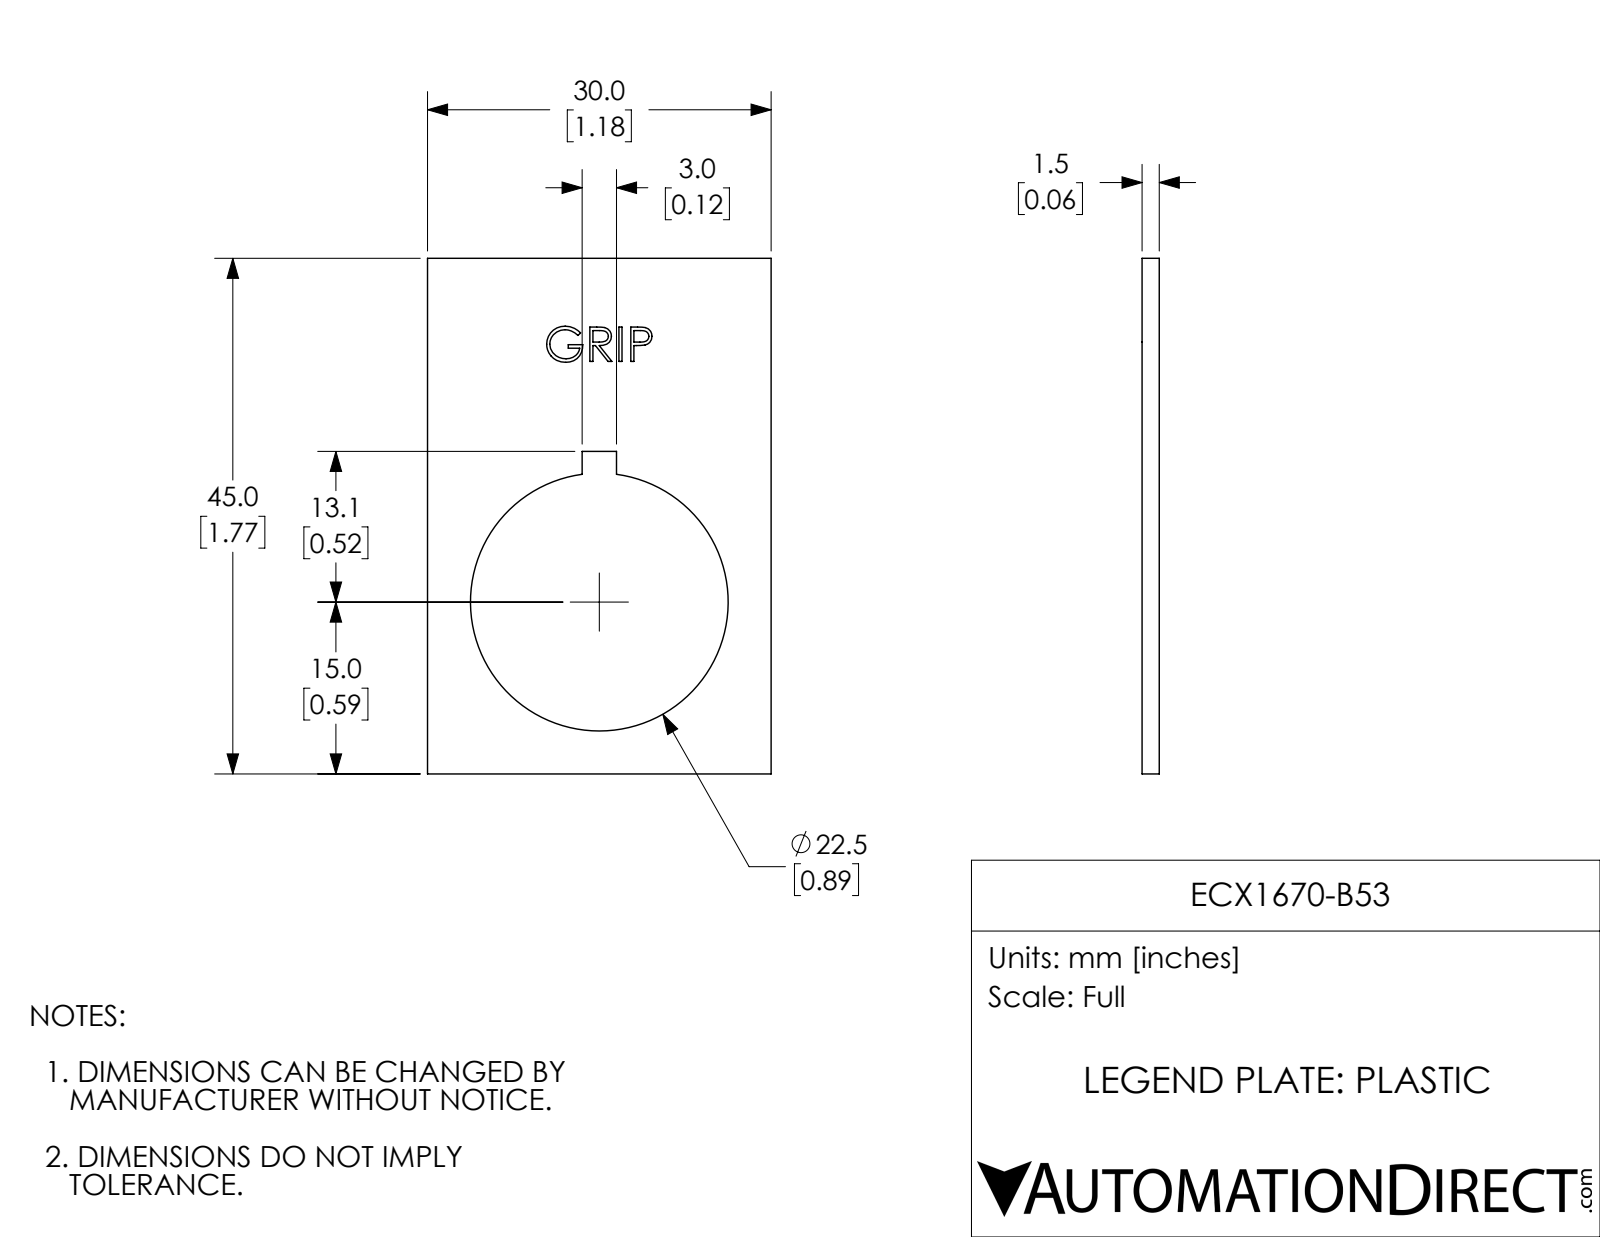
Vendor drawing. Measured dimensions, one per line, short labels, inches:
name: ECX1670-B53
written by: SolidWorks 2017 (AUTOMOTIVE_DESIGN)
unit: in
bodies: 1 solid, 65 faces (42 planar, 3 cylindrical, 20 other)
size: 1.772 × 1.181 × 0.059
volume: 0.087 in³; area: 3.459 in²
holes: 1× ⌀0.886
face distances: 0.059, 1.181, 1.772, 0.058, 0.531, 0.65, 1.108, 0.663, 0.118, 0.041
